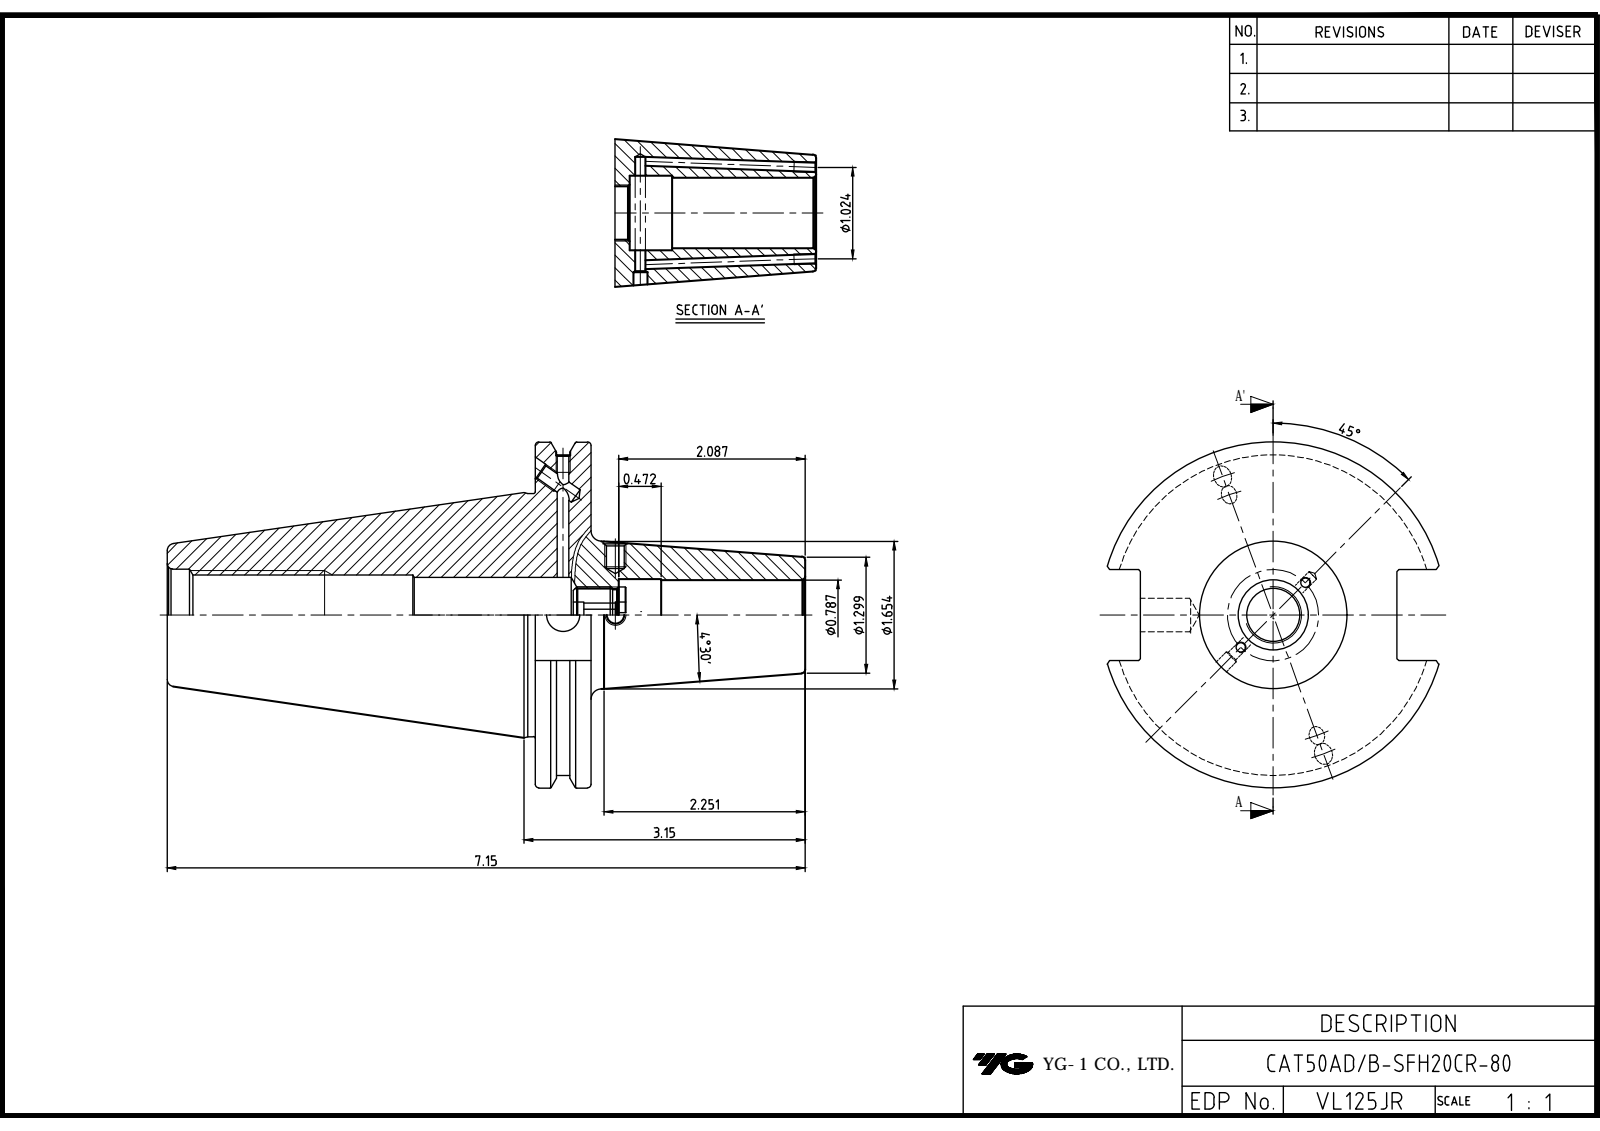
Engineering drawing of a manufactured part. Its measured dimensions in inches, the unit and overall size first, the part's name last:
Units: inches
Overall size (bounding box): 7.15 × 3.875 × 3.728
Round holes (diameter × count): ⌀0.097 ×2, ⌀0.128 ×2, ⌀0.163 ×2, ⌀0.165 ×2, ⌀0.197 ×2, ⌀0.375 ×1, ⌀0.587 ×1, ⌀0.787 ×1, ⌀0.811 ×1, ⌀0.846 ×1, ⌀0.865 ×1, ⌀1.031 ×1
Round bosses / shafts (diameter × count): ⌀3.875 ×1, ⌀3.594 ×1, ⌀2.726 ×1, ⌀1.654 ×1
Main face-to-face distances: 0.625, 4.125, 4.75, 7.15, 3.025, 2.4, 2.875, 1.02, 4.513, 0.389
Volume: 22.56 in³ · Surface area: 86.59 in²
Bodies: 1 solid, 90 faces (37 planar, 29 cylindrical, 24 other)
Part name (STEP PRODUCT): LO-CAT50ADB-SFH20CR-80
STEP written by: Autodesk Inventor 2025 (AUTOMOTIVE_DESIGN)
